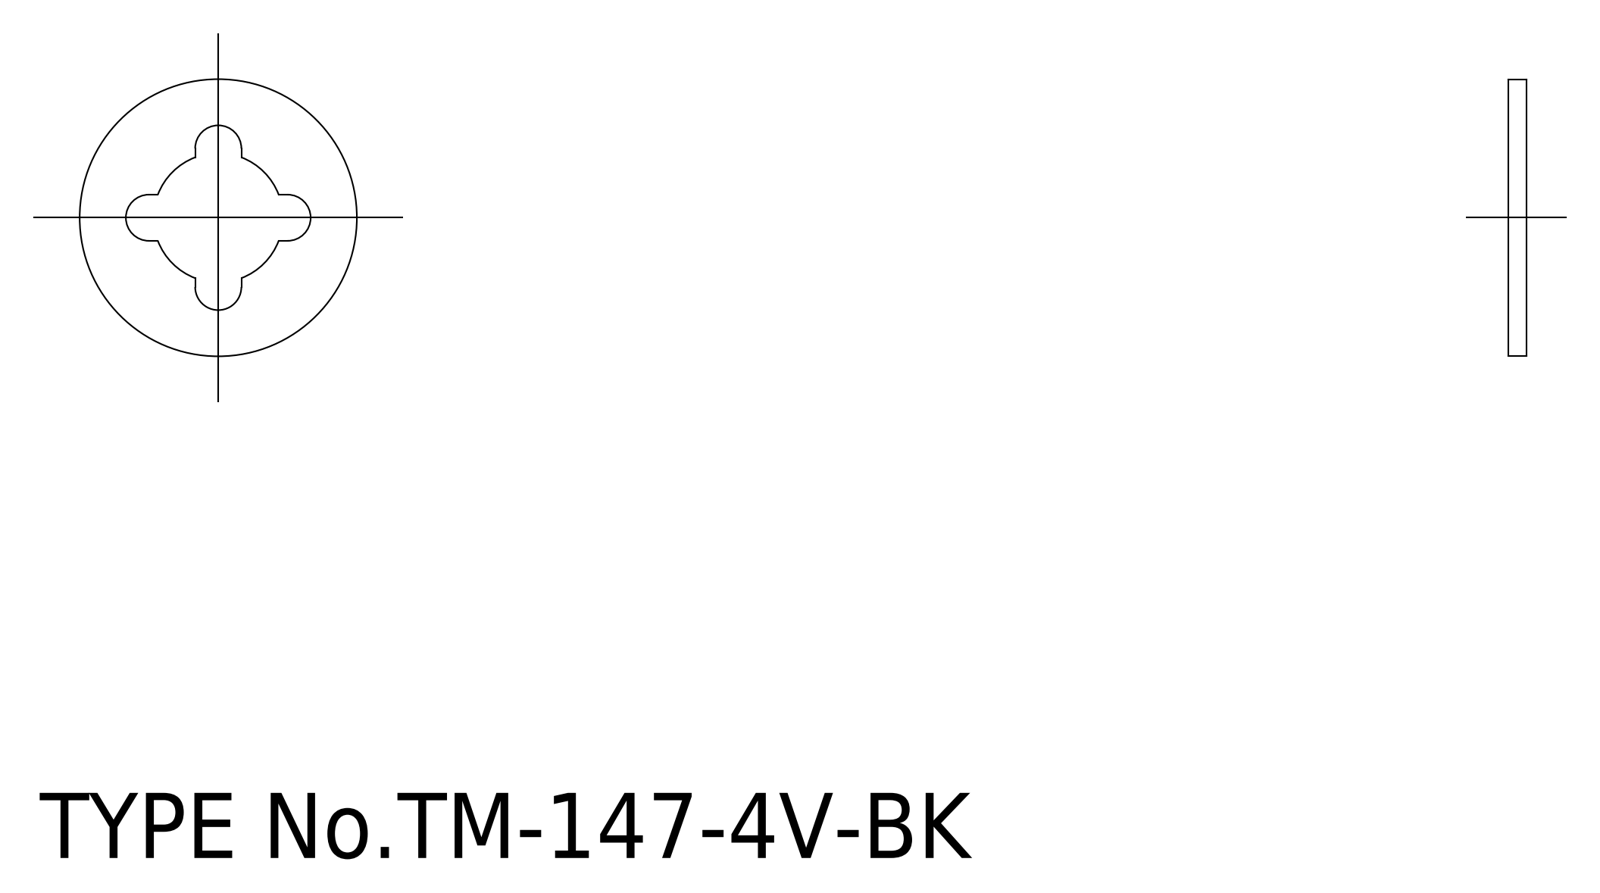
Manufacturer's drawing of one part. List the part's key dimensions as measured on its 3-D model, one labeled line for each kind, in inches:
STEP written by: spGate 19.8.4 (****-****-****-****) (AUTOMOTIVE_DESIGN)
Units: inches
Bodies: 1 solid, 20 faces (10 planar, 10 cylindrical, 0 other)
Overall size (bounding box): 0.472 × 0.472 × 0.031
Volume: 0.004 in³ · Surface area: 0.326 in²
Round bosses / shafts (diameter × count): ⌀0.472 ×1
Partial cylindrical surfaces — rounded edges, fillets, slot ends (radius × count): R0.039 ×4, R0.11 ×1
Main face-to-face distances: 0.031, 0.079
